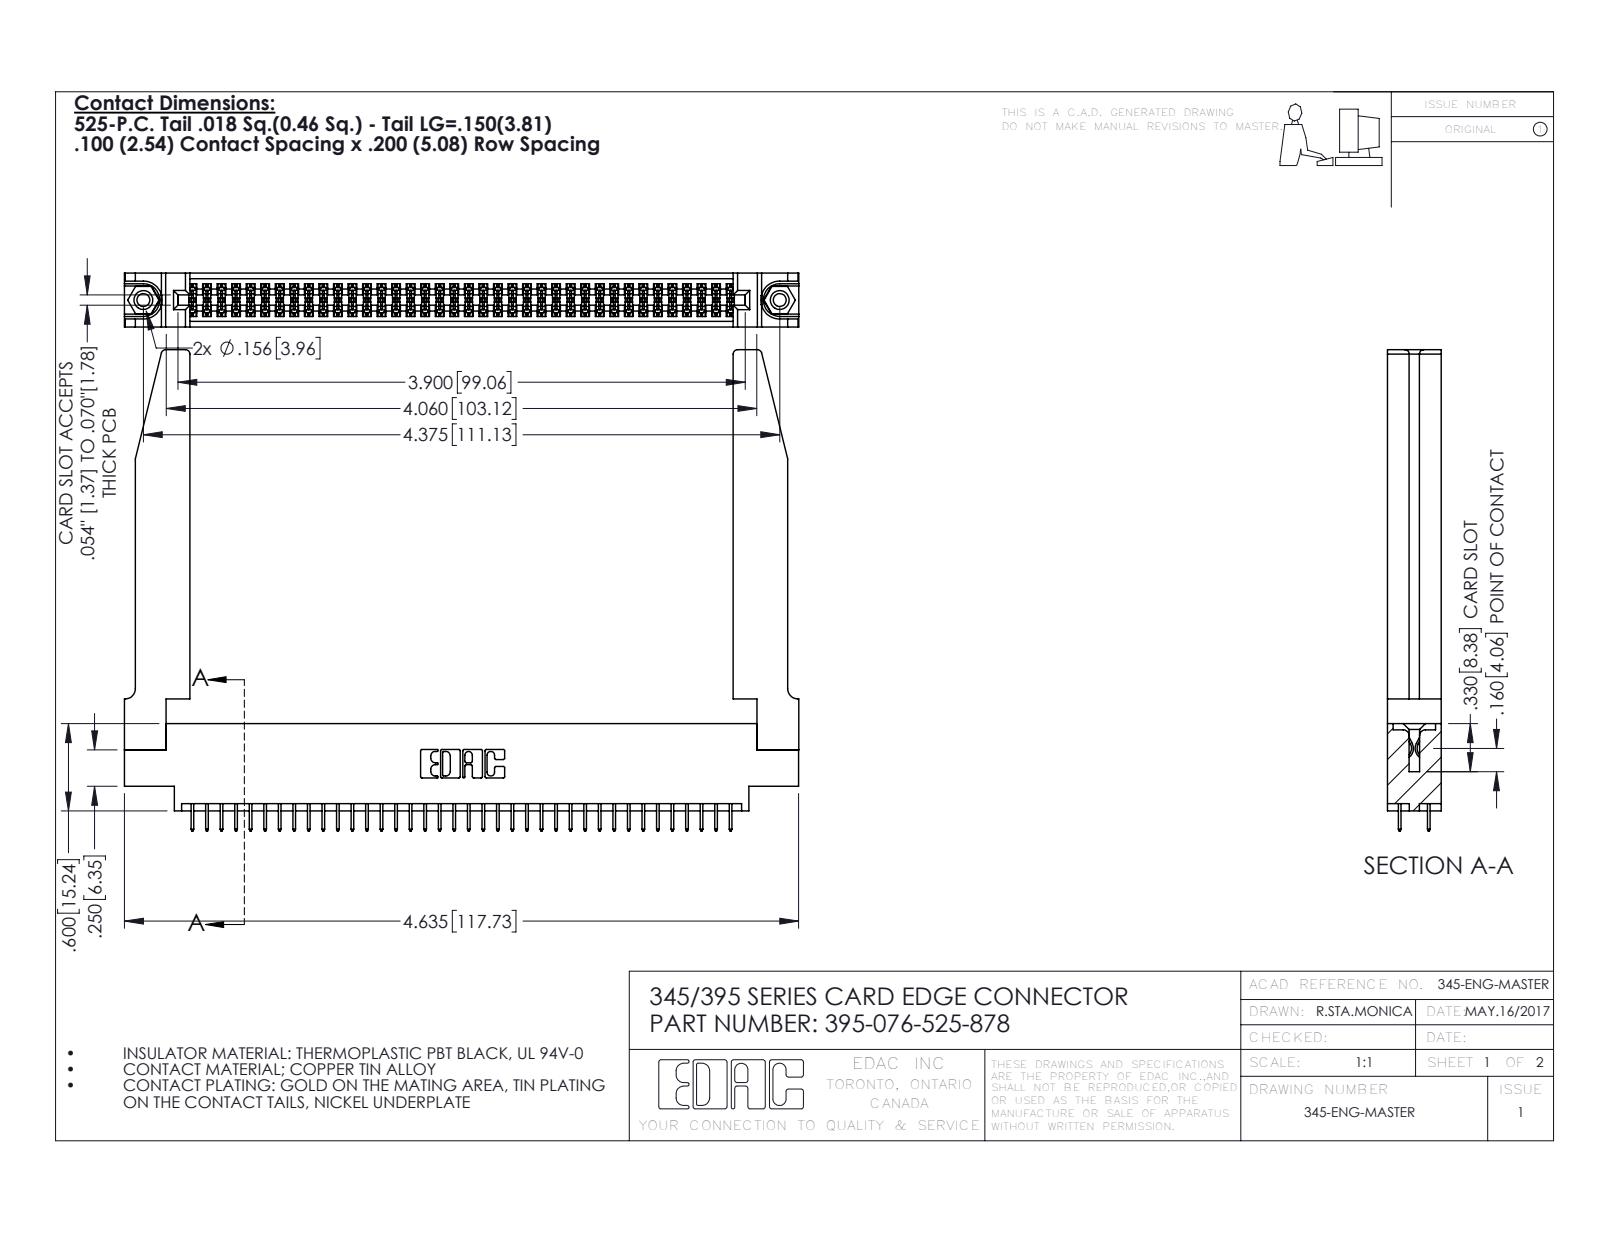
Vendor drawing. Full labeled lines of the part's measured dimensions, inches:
Part name (STEP PRODUCT): 345 Part_0.170 Offset - 0.156 Dia-TH; 345-292-001_345-293-125; 395-076-525-878; 345-220-078_345-220-078 (+1 more)
STEP written by: SolidWorks 2020 (CONFIG_CONTROL_DESIGN)
Units: inches
Bodies: 81 solids, 4468 faces (3190 planar, 1226 cylindrical, 52 other)
Overall size (bounding box): 4.636 × 3.307 × 0.37
Volume: 1.155 in³ · Surface area: 35.69 in²
Round holes (diameter × count): ⌀0.089 ×2, ⌀0.125 ×2, ⌀0.156 ×2, ⌀0.064 ×1
Round bosses / shafts (diameter × count): ⌀0.155 ×2
Partial cylindrical surfaces — rounded edges, fillets, slot ends (radius × count): R0.006 ×114, R0.01 ×22, R0.03 ×8, R0.007 ×6, R0.031 ×6, R0.026 ×3, R0.014 ×2, R0.019 ×2
Main face-to-face distances: 0.37, 0.072, 0.298, 0.098, 0.272, 0.025, 0.2, 0.225, 0.148, 0.15
Hole centre spacings: 0.27, 4.139, 4.375
